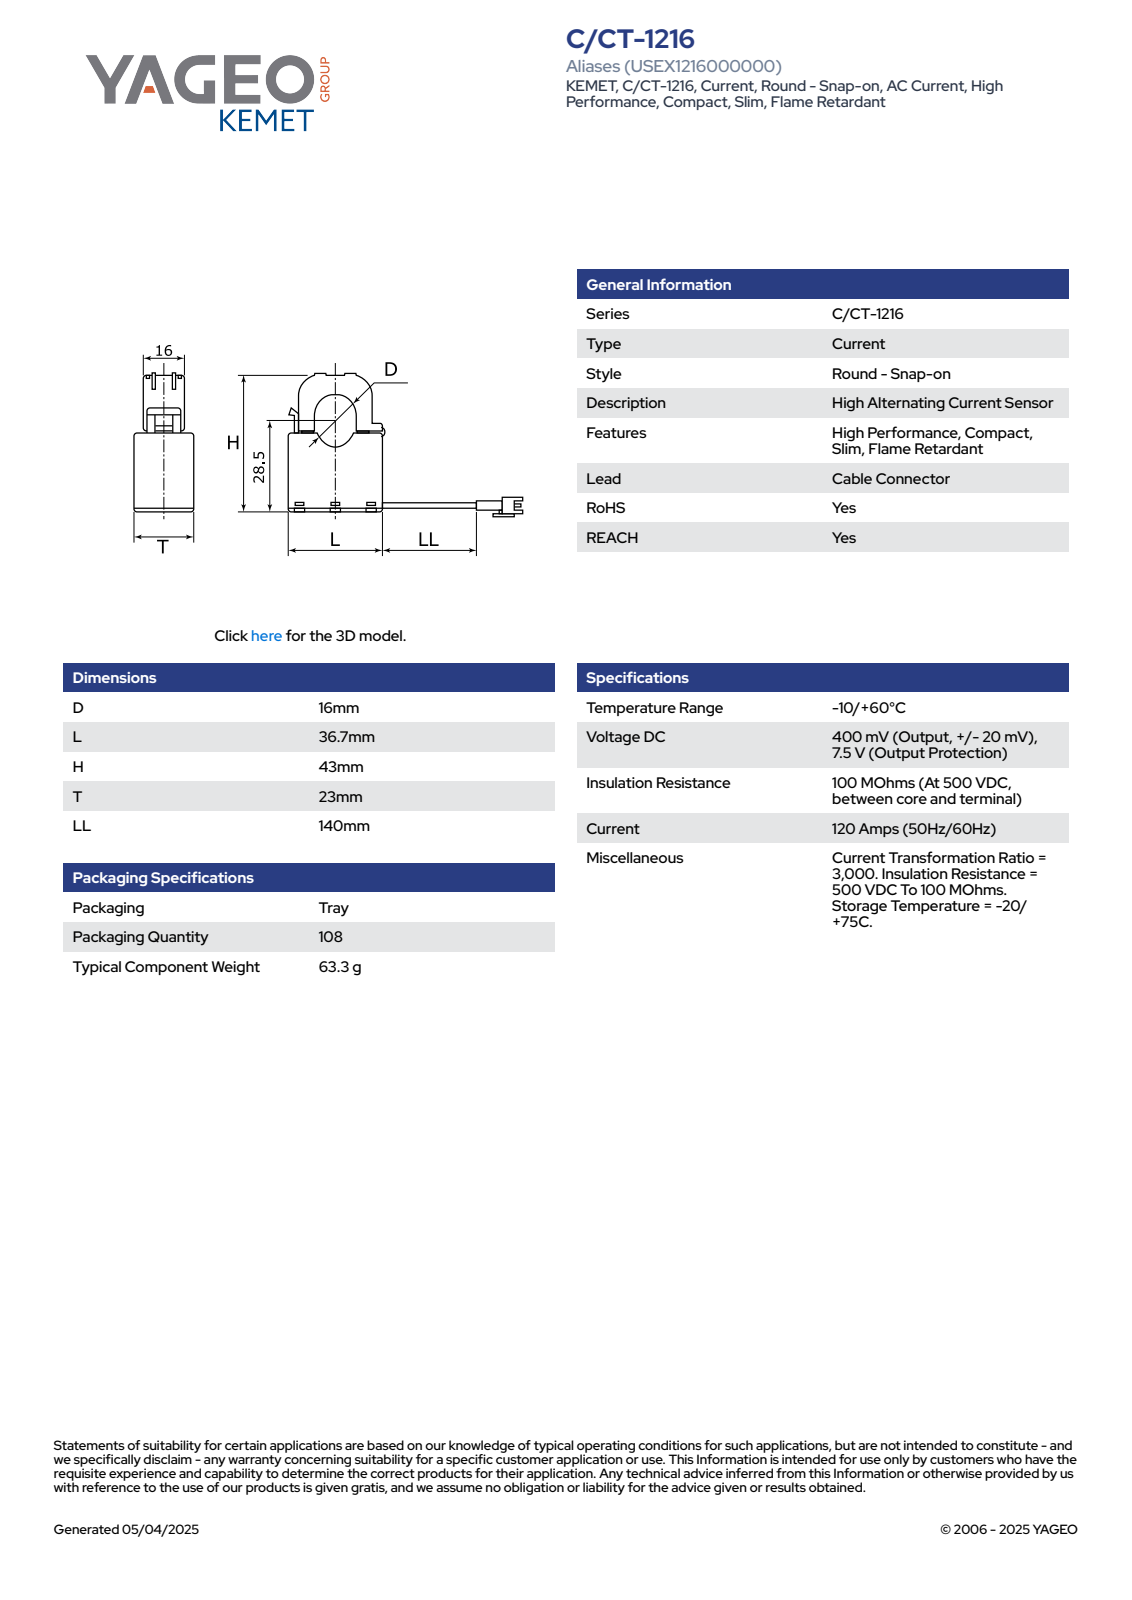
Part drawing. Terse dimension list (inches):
name: Default
written by: SolidWorks 2014 (AUTOMOTIVE_DESIGN)
unit: in
bodies: 2 solids, 150 faces (108 planar, 34 cylindrical, 8 other)
size: 7.232 × 1.693 × 0.906
volume: 1.296 in³; area: 11.21 in²
bosses: 1× ⌀0.039
rounds: 9× R0.039, 8× R0.012, 4× R0.004, 4× R0.059, 2× R0.276, 2× R0.315
face distances: 0.138, 0.768, 0.906, 0.63, 0.807, 1.445, 0.407, 1.037, 0.266, 1.179
